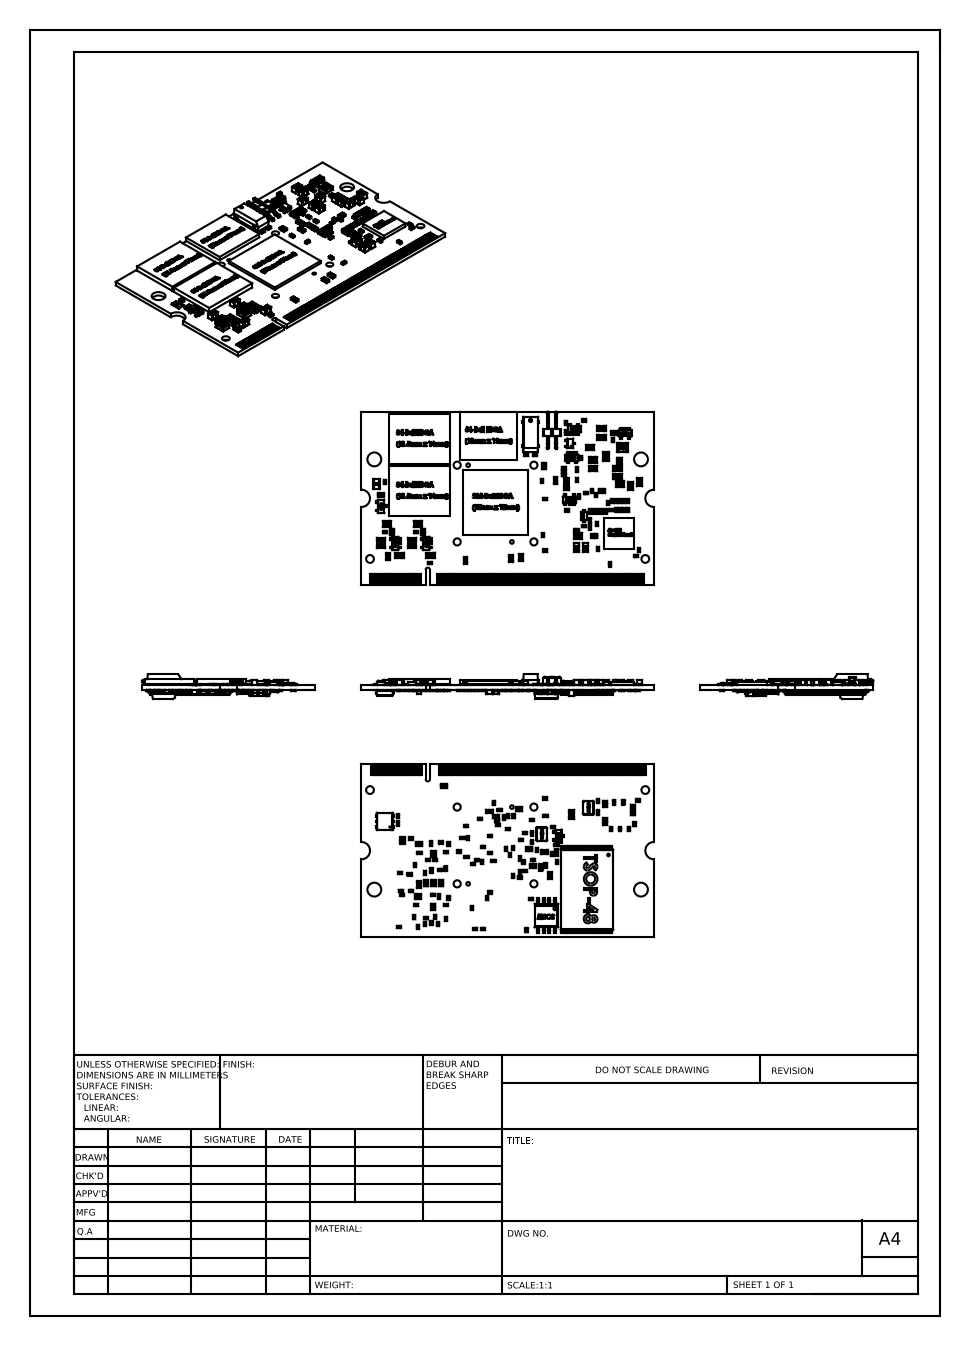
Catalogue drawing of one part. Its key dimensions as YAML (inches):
part_name: "R0402_H0.35; SOT323(SC70); 48-QFN (7mm x 7mm); TSOP48-1 (+8 more)"
step_written_by: "SolidWorks 2014 (AUTOMOTIVE_DESIGN)"
units: inches
bodies: {solids: 313, faces: 40592, planar: 18986, cylindrical: 4979, other: 16627}
overall_size: [2.661, 1.575, 0.223]
volume: 0.25
surface_area: 14.55
round_holes:
  - {diameter: 0.065, count: 4}
  - {diameter: 0.033, count: 2}
  - {diameter: 0.071, count: 2}
  - {diameter: 0.126, count: 2}
  - {diameter: 0.012, count: 1}
  - {diameter: 0.024, count: 1}
  - {diameter: 0.028, count: 1}
partial_cylinders:
  - {radius: 0.008, count: 48}
  - {radius: 0.004, count: 19}
  - {radius: 0.014, count: 5}
  - {radius: 0.01, count: 4}
  - {radius: 0.011, count: 4}
  - {radius: 0.02, count: 3}
  - {radius: 0.012, count: 2}
  - {radius: 0.016, count: 2}
face_to_face_distances: [0.039, 0.047, 0.096, 0.057, 0.087, 0.075, 0.047, 0.021, 0.043, 0.036]
hole_center_spacings: [0.698, 0.906, 0.987, 2.626, 0.1, 0.2, 0.296, 0.382]
